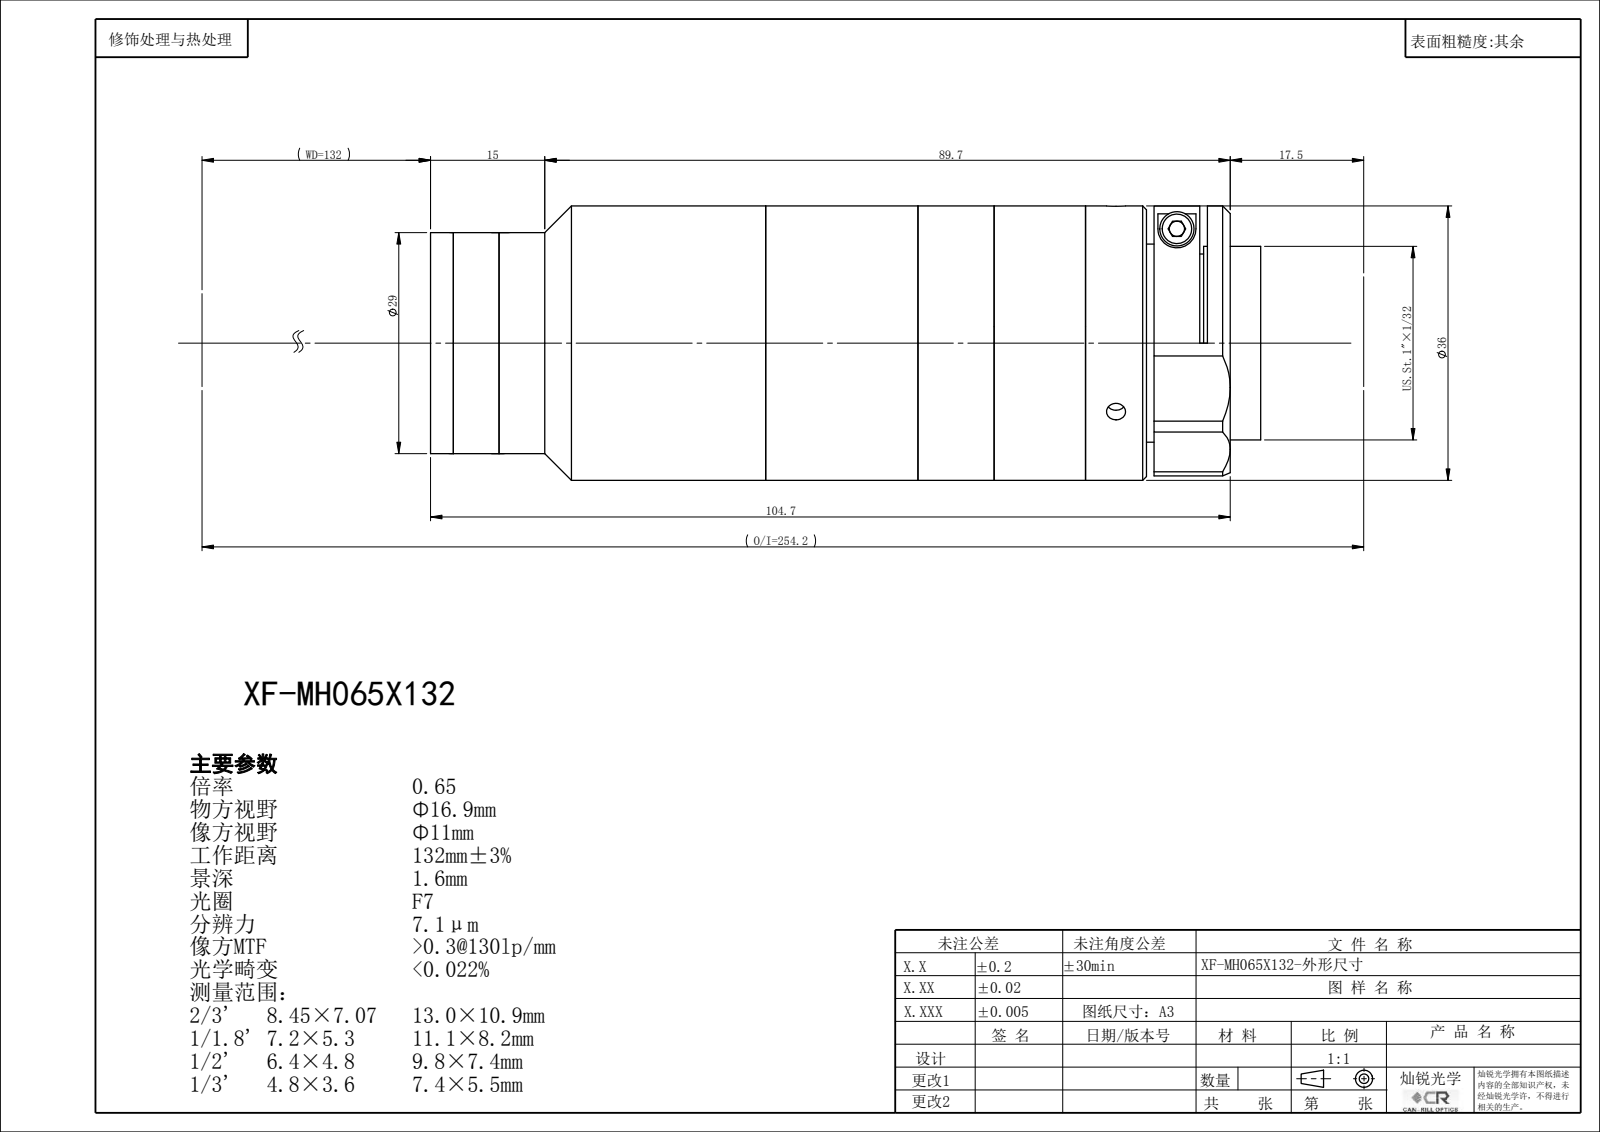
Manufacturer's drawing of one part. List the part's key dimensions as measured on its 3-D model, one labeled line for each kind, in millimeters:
Part name (STEP PRODUCT): XF-MH065X132
STEP written by: SolidWorks 2022 (CONFIG_CONTROL_DESIGN)
Units: millimetres
Bodies: 0 solids, 128 faces (64 planar, 42 cylindrical, 22 other)
Overall size (bounding box): 108.75 × 36 × 36
Round holes (diameter × count): ⌀2.5 ×3, ⌀18 ×1, ⌀22.4 ×1, ⌀24 ×1, ⌀24.9 ×1, ⌀26.4 ×1
Round bosses / shafts (diameter × count): ⌀36 ×1, ⌀34 ×1, ⌀29 ×1, ⌀25.4 ×1
Main face-to-face distances: 1.5, 20, 59.25, 60.75, 39.25, 40.75, 99.75, 48, 28, 11.25
